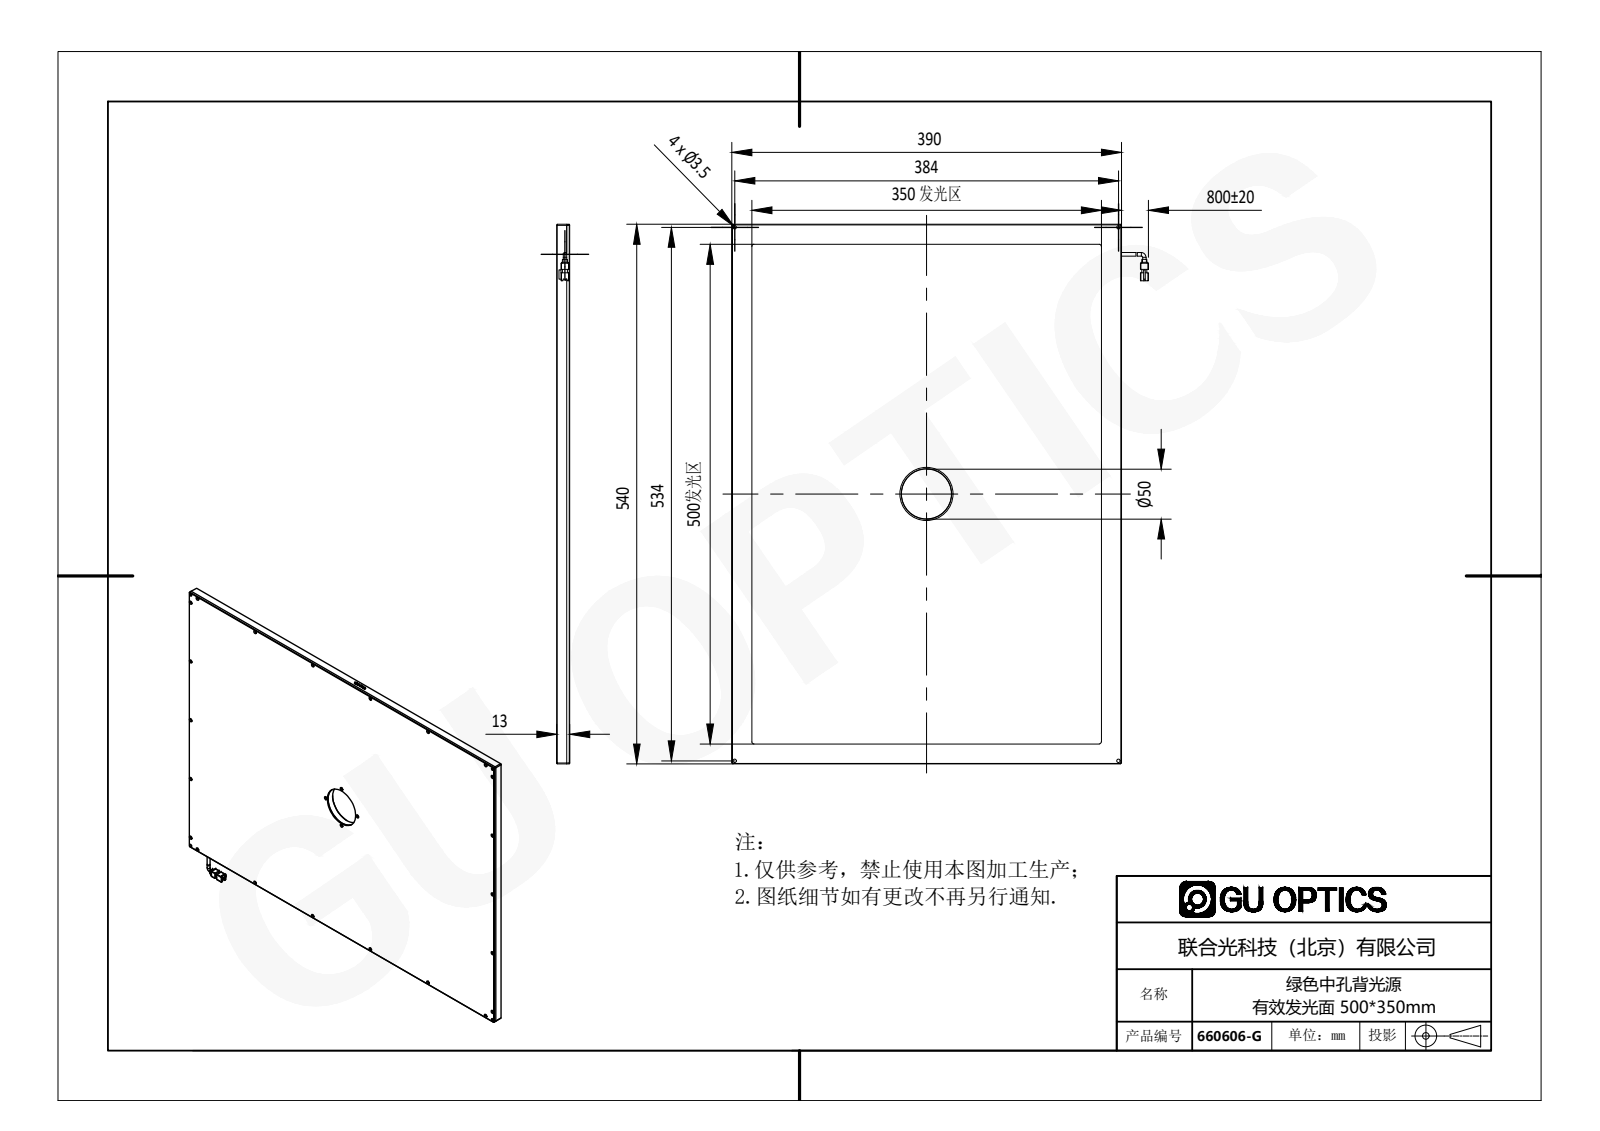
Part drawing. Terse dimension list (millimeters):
name: 660606-G
written by: SolidWorks 2016 (AUTOMOTIVE_DESIGN)
unit: mm
bodies: 7 solids, 987 faces (622 planar, 204 cylindrical, 161 other)
size: 540 × 417 × 13
volume: 2 085 000 mm³; area: 943 357 mm²
holes: 26× ⌀2, 22× ⌀1.6, 22× ⌀2.4, 4× ⌀3.5, 1× ⌀50, 1× ⌀53, 1× ⌀60.2
bosses: 2× ⌀3.5, 1× ⌀60
rounds: 8× R0.5, 6× R1, 4× R1.5, 4× R2
face distances: 6.5, 3, 9.5, 13, 3.5, 10, 2, 6, 8, 384
hole spacings: 102, 397.32, 12, 90, 204, 384, 434.82, 541.53
